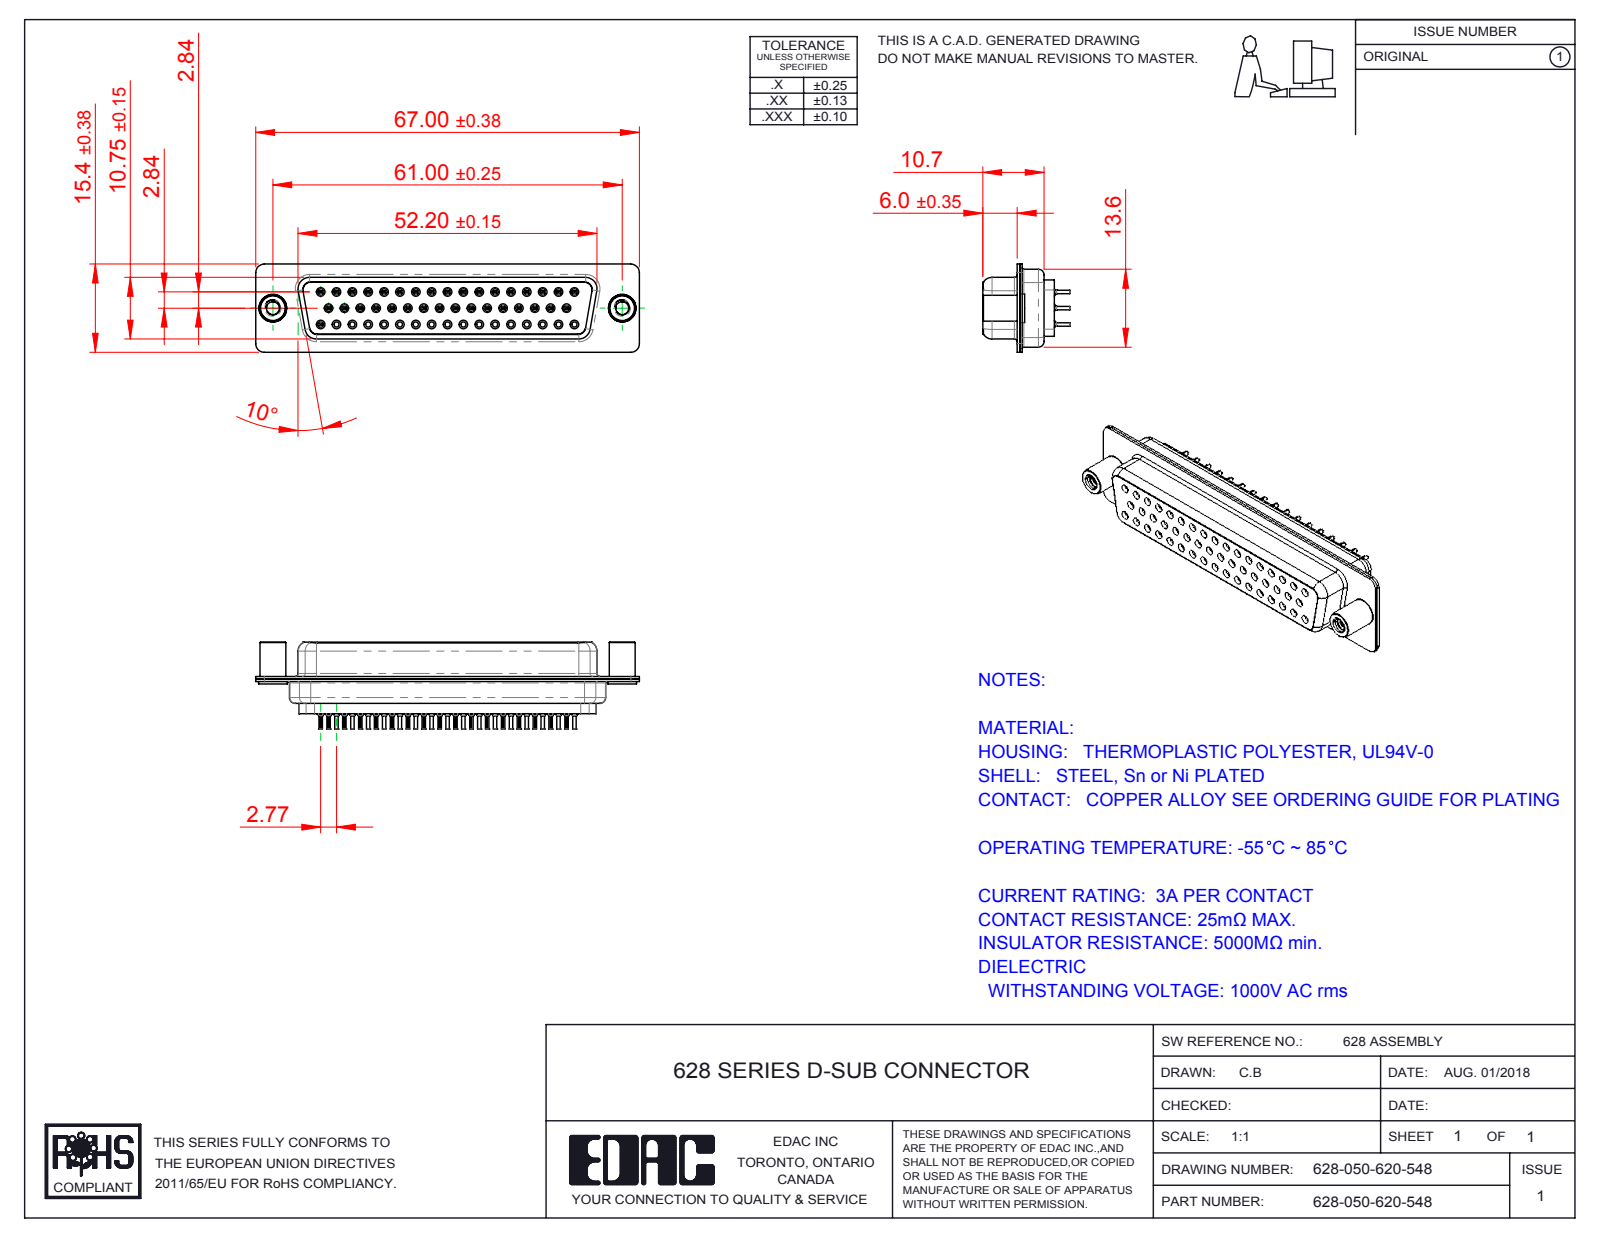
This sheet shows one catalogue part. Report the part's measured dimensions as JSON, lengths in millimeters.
{"part_name": "628 Housing_50 LP; 628-050-620-548; 628 Contact Row 1_20L; 628 Contact Row 3_20L (+4 more)", "step_written_by": "SolidWorks 2016 (CONFIG_CONTROL_DESIGN)", "units": "millimeters", "bodies": {"solids": 39, "faces": 4839, "planar": 1171, "cylindrical": 1415, "other": 2253}, "overall_size": [67, 15.4, 15.2], "volume_mm3": 6643, "surface_area_mm2": 13786, "round_holes": [[0.9, 50], [1.6, 50], [0.2, 34], [0.8, 34], [1.1, 34], [1.7, 17], [1.5, 16], [2, 16], [2.26, 2], [4, 2], [4.8, 2]], "round_bosses_or_shafts": [[2, 34], [1.5, 34], [1.2, 34], [0.6, 34], [5, 2], [4.9, 2], [4.5, 2]], "partial_cylinders_radius": [[0.1, 68], [0.28, 33], [1.5, 16], [2, 12], [1.35, 8], [0.25, 4], [0.5, 4], [0.6, 4]], "face_to_face_distances": [0.45, 0.4, 0.9, 10.3, 6.05, 6.5, 6.45, 6, 12.5, 11.33], "hole_center_spacings": [3.16, 2.77, 5.54, 8.31, 11.08, 13.85, 16.62, 19.39]}
